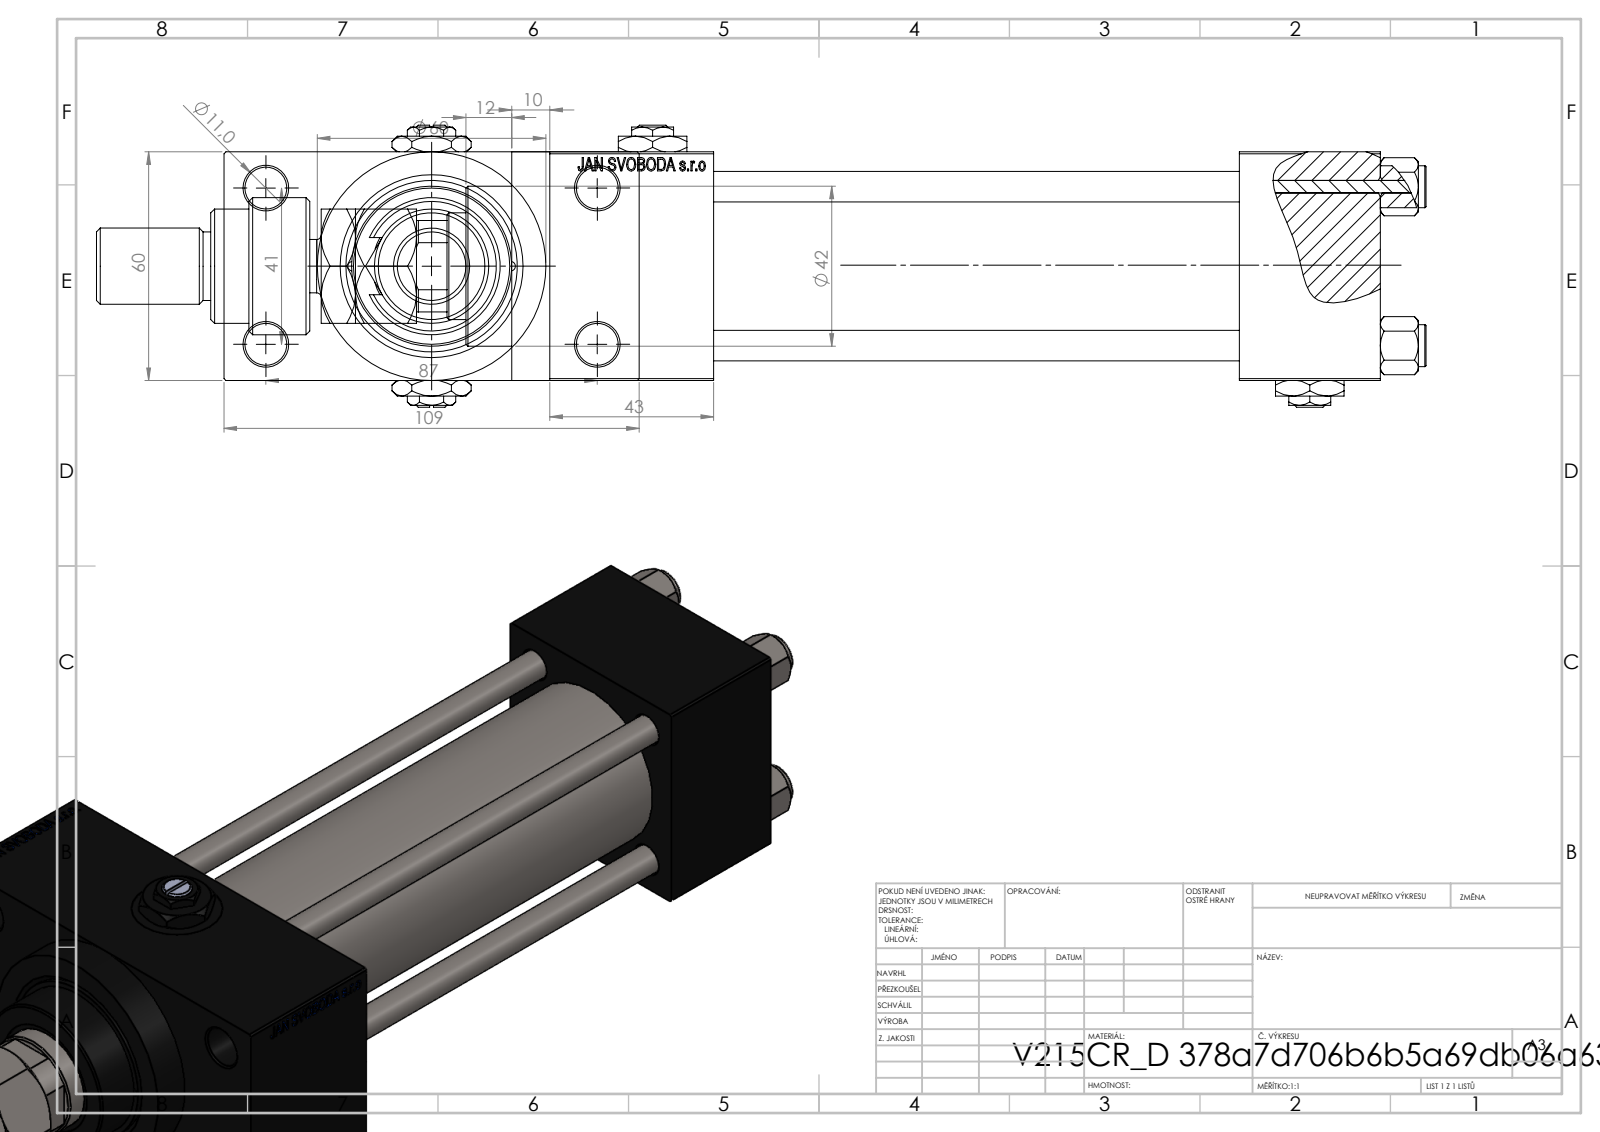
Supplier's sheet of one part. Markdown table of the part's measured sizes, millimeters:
| quantity | value |
| --- | --- |
| part name | V215CR_D_Body; V215CR_VCP_D; FEMALE_PART_FOR_DFA; V215CR_D_TYCINKA (+4 more) |
| STEP written by | SolidWorks 2019 (CONFIG_CONTROL_DESIGN) |
| units | millimeters |
| bodies | 15 solids, 1284 faces (574 planar, 106 cylindrical, 604 other) |
| overall size | 349 × 109 × 74 |
| volume | 683 499 mm³ |
| surface area | 179 541 mm² |
| round holes (diameter × count) | 8 × 4, 11 × 4, 2.5 × 2, 7 × 2, 16.66 × 2, 24 × 2, 18.5 × 1, 28 × 1, 31 × 1, 40 × 1, 45 × 1 |
| round bosses / shafts (diameter × count) | 11 × 4, 60 × 1, 46 × 1, 42 × 1, 36 × 1, 30 × 1, 22 × 1, 20 × 1 |
| partial cylindrical surfaces (radius × count) | 7.5 × 1, 12 × 1, 13.5 × 1 |
| main face-to-face distances | 60, 24.5, 84.5, 138, 37, 175, 43, 218, 181, 109 |
| hole center spacings | 20.85, 22.65, 29.49, 30.62, 41.7, 46.53, 47.15, 48.09 |
